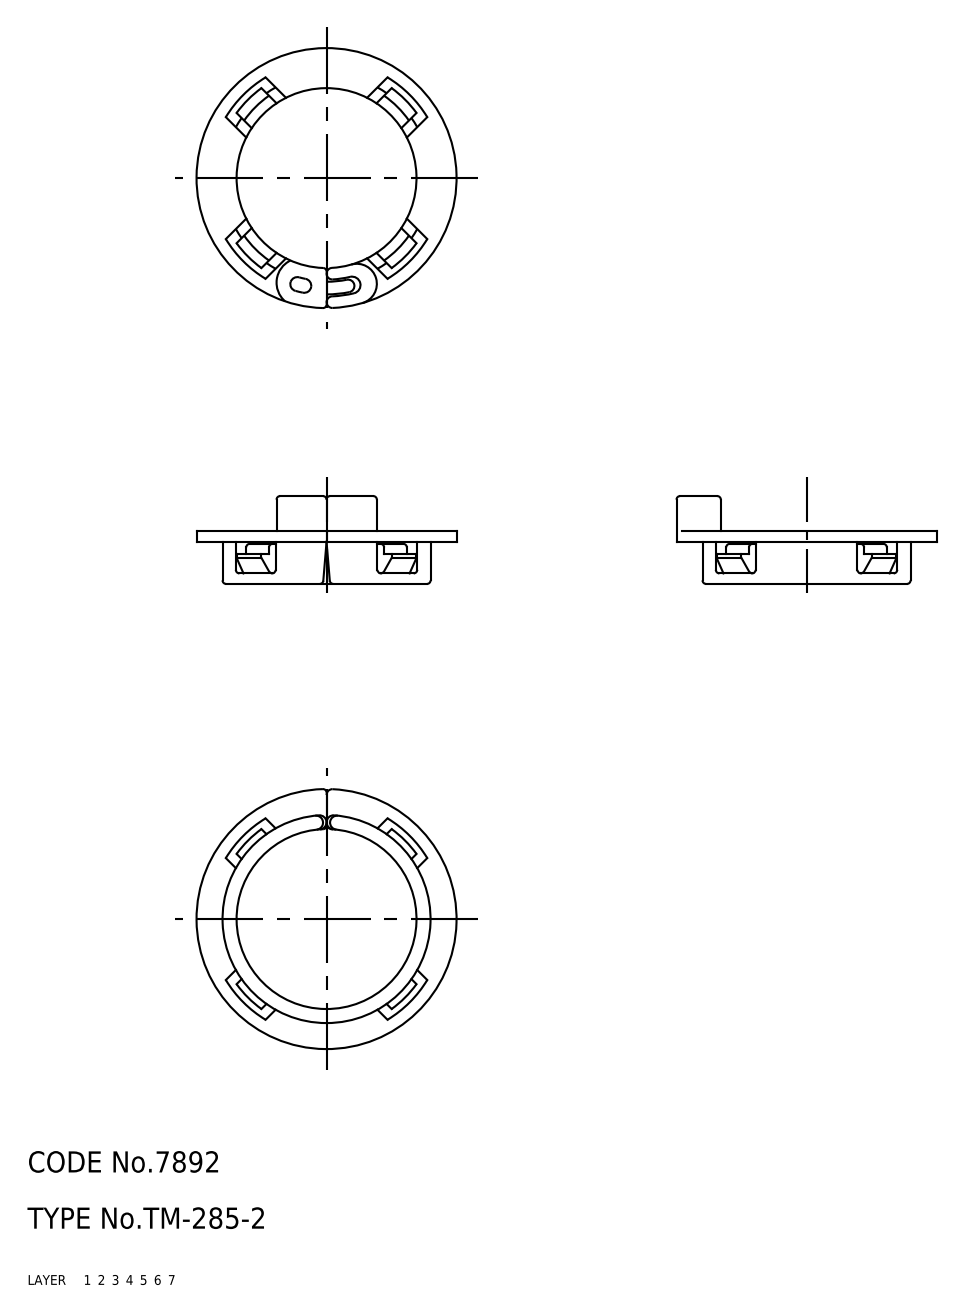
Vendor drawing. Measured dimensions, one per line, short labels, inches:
name: grommet
written by: CADfix (AUTOMOTIVE_DESIGN)
unit: in
bodies: 1 solid, 111 faces (0 planar, 0 cylindrical, 111 other)
size: 1.457 × 1.456 × 0.492
volume: 0.114 in³; area: 4.166 in²
